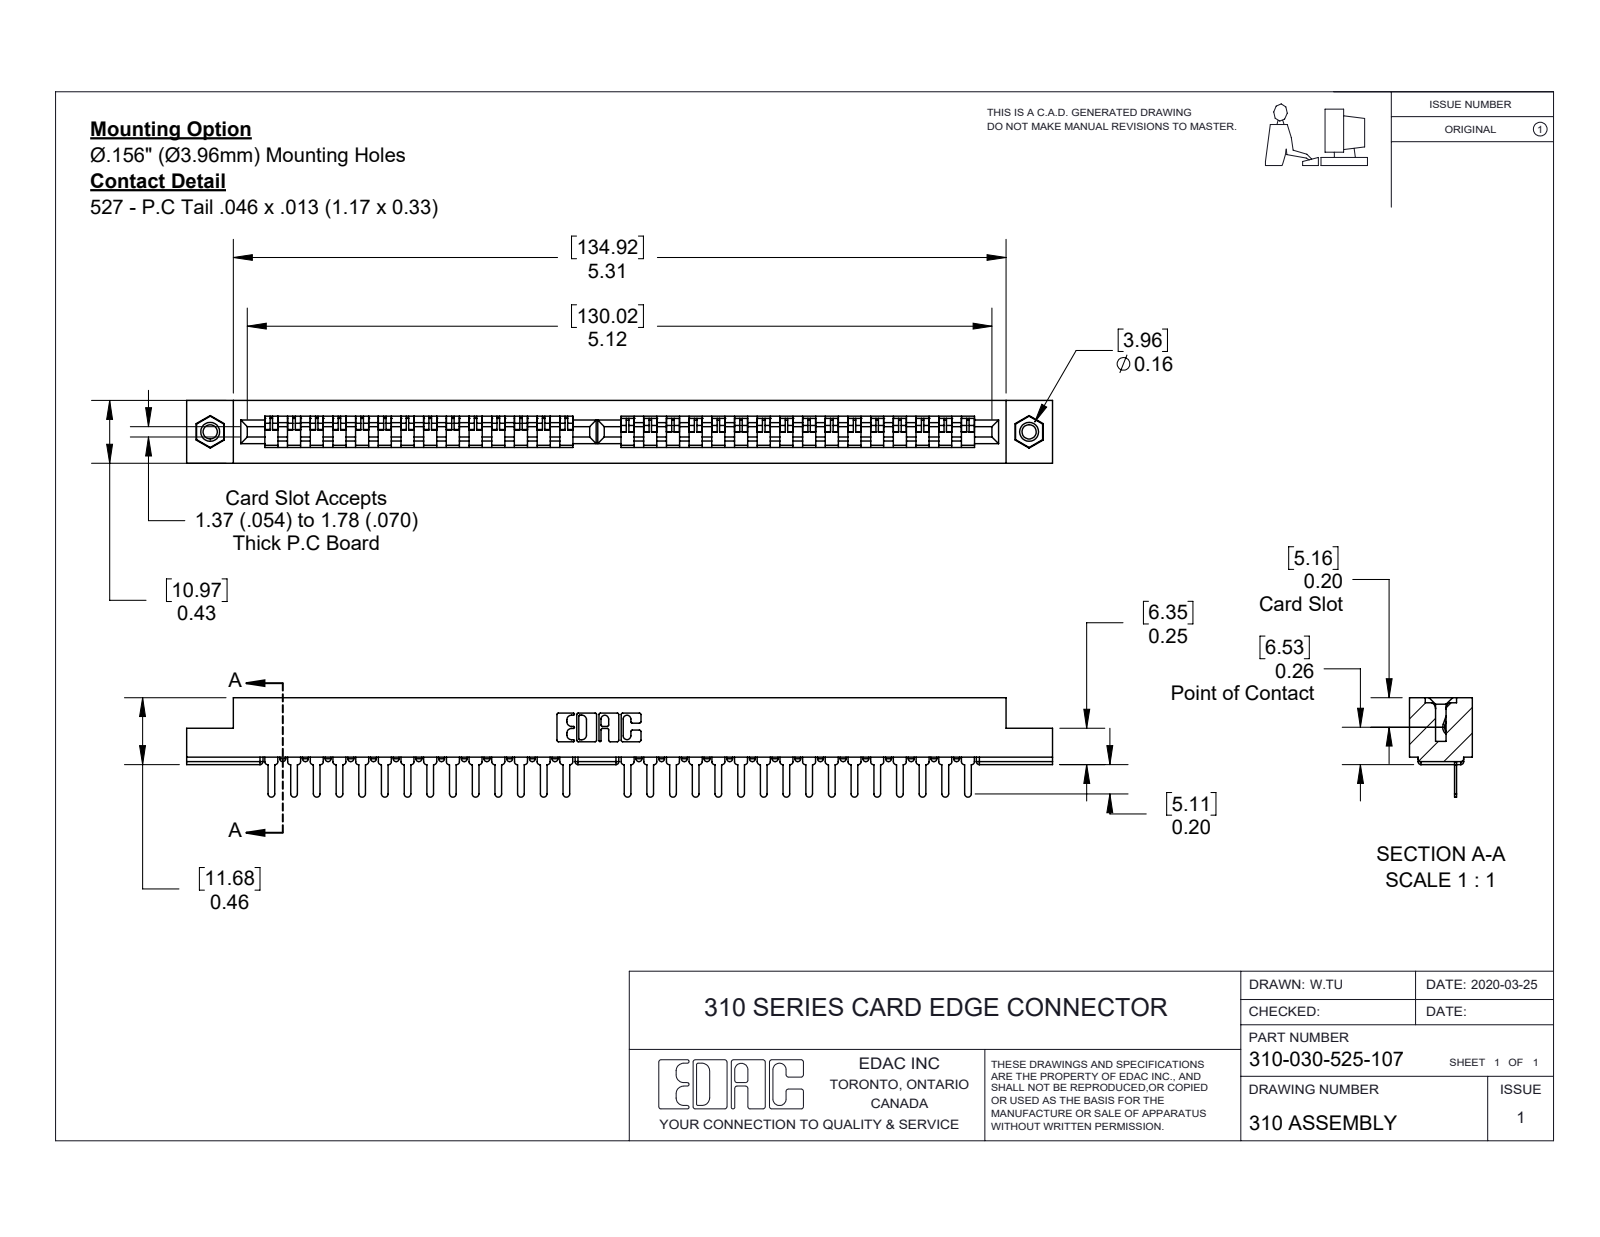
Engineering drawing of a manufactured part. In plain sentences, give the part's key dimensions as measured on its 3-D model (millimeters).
The part is named "310 Part_.116 Hex; 310-030-525-107; 345-250-001_345-250-005-103; 307-290-001_525". Its 3-D file was written by "SolidWorks 2016 (CONFIG_CONTROL_DESIGN)". It is 33 solids with 1906 faces: 1226 planar, 600 cylindrical and 80 other. Overall it measures 151.21 by 17.37 by 10.97 millimeters. Its volume is 12 632 cubic millimeters and its surface area 14 856 square millimeters. Round holes: 2 of diameter 2.5, 2 of diameter 3.17, 2 of diameter 3.96. Round bosses or shafts: 2 of diameter 3.94. Partial cylindrical surfaces (rounded edges, fillets, slot ends): 158 of radius 0.51, 30 of radius 0.58, 22 of radius 0.25, 6 of radius 0.17, 6 of radius 0.8, 3 of radius 0.67, 2 of radius 0.3, 2 of radius 0.64. The main face-to-face distances are 2.76, 8.22, 10.98, 0.38, 1.82, 0.33, 10.38, 5.46, 6.4, 4.58. The hole center spacings are 143.
